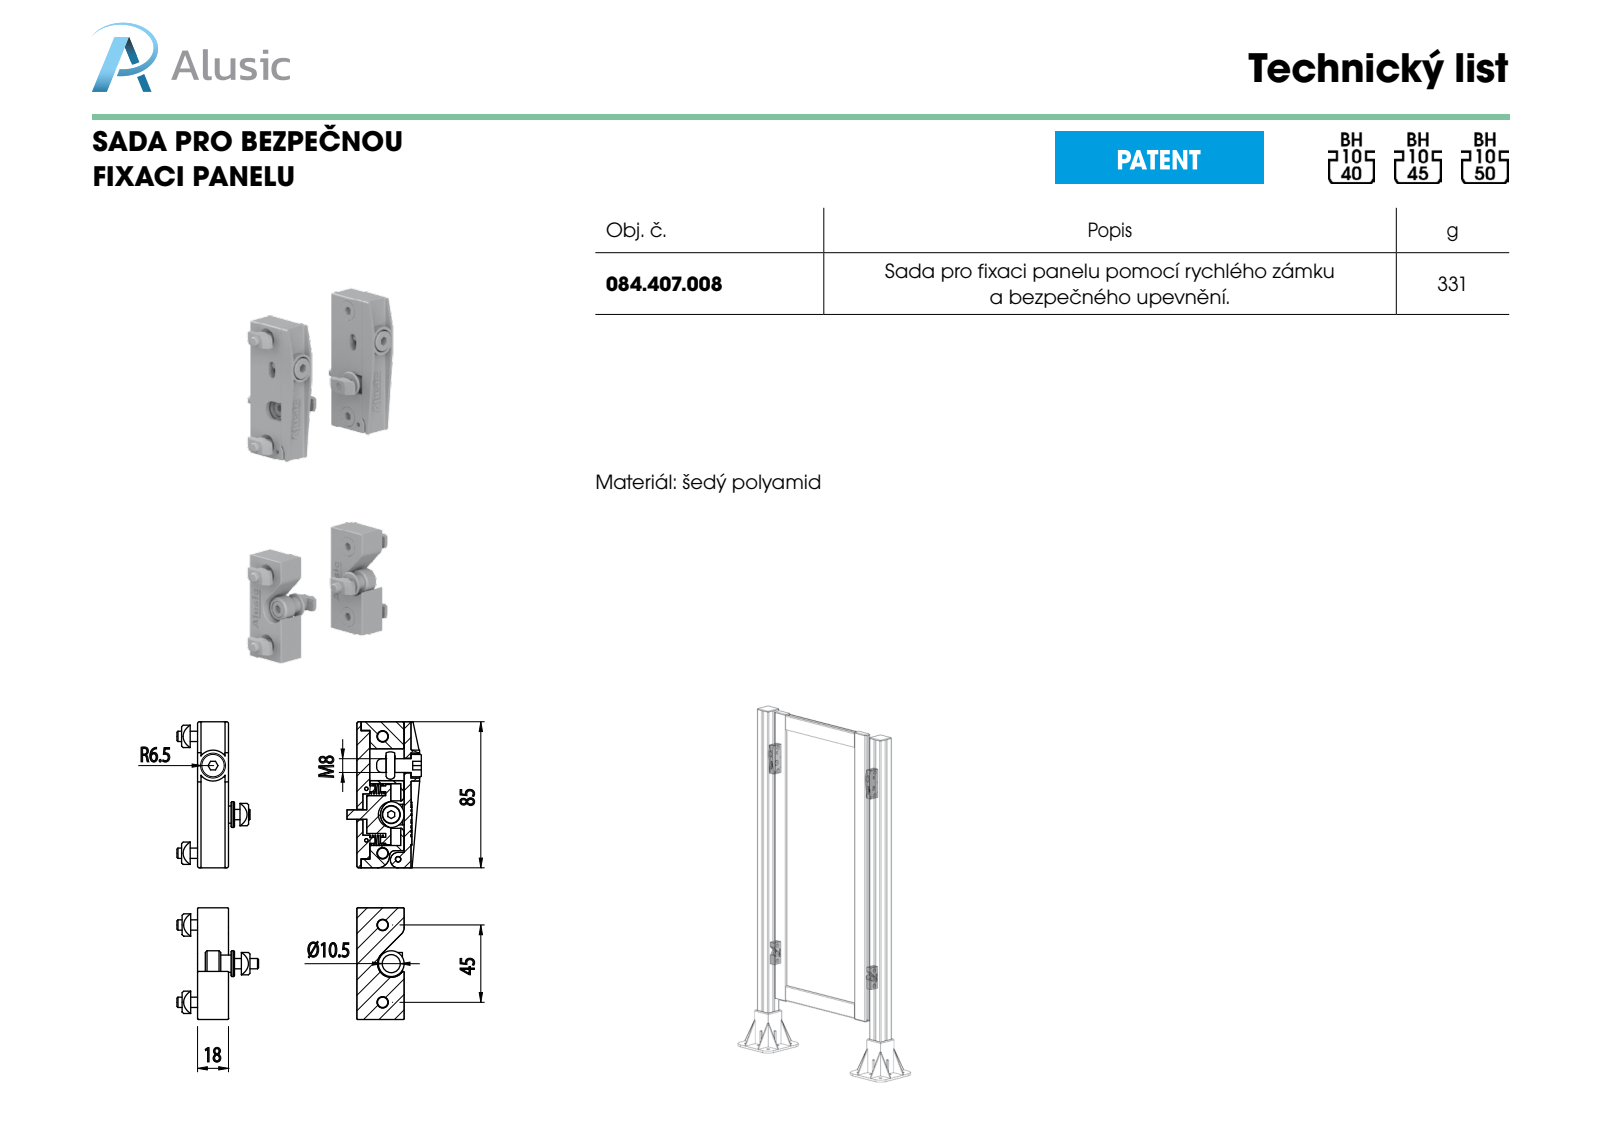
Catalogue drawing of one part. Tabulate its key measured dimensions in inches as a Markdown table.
| quantity | value |
| --- | --- |
| part name | 084.407.103-6; 084.407.103-3; VITI TCEI UNI 5931_M6x25 UNI 5931; 084.407.103-2 (+8 more) |
| STEP written by | SolidWorks 2016 (CONFIG_CONTROL_DESIGN) |
| units | inches |
| bodies | 52 solids, 3582 faces (2384 planar, 938 cylindrical, 260 other) |
| overall size | 8.465 × 4.882 × 2.235 |
| volume | 10.07 in³ |
| surface area | 146.1 in² |
| round holes (diameter × count) | 0.197 × 14, 0.26 × 12, 0.079 × 4, 0.413 × 4, 0.118 × 2, 0.126 × 2, 0.217 × 2, 0.236 × 2, 0.335 × 2, 0.571 × 2 |
| round bosses / shafts (diameter × count) | 0.236 × 12, 0.472 × 8, 0.315 × 8, 0.591 × 4, 0.394 × 4, 0.138 × 4, 0.512 × 2, 0.217 × 2 |
| partial cylindrical surfaces (radius × count) | 0.02 × 50, 0.039 × 40, 0.118 × 26, 0.197 × 26, 0.01 × 12, 0.012 × 12, 0.022 × 12, 0.028 × 12 |
| main face-to-face distances | 3.228, 0.444, 0.709, 0.236, 1.083, 0.098, 0.984, 2.52, 3.937, 0.472 |
| hole center spacings | 0.444, 0.907, 0.821, 1.122, 4.178, 5.059, 5.078, 0.92 |
